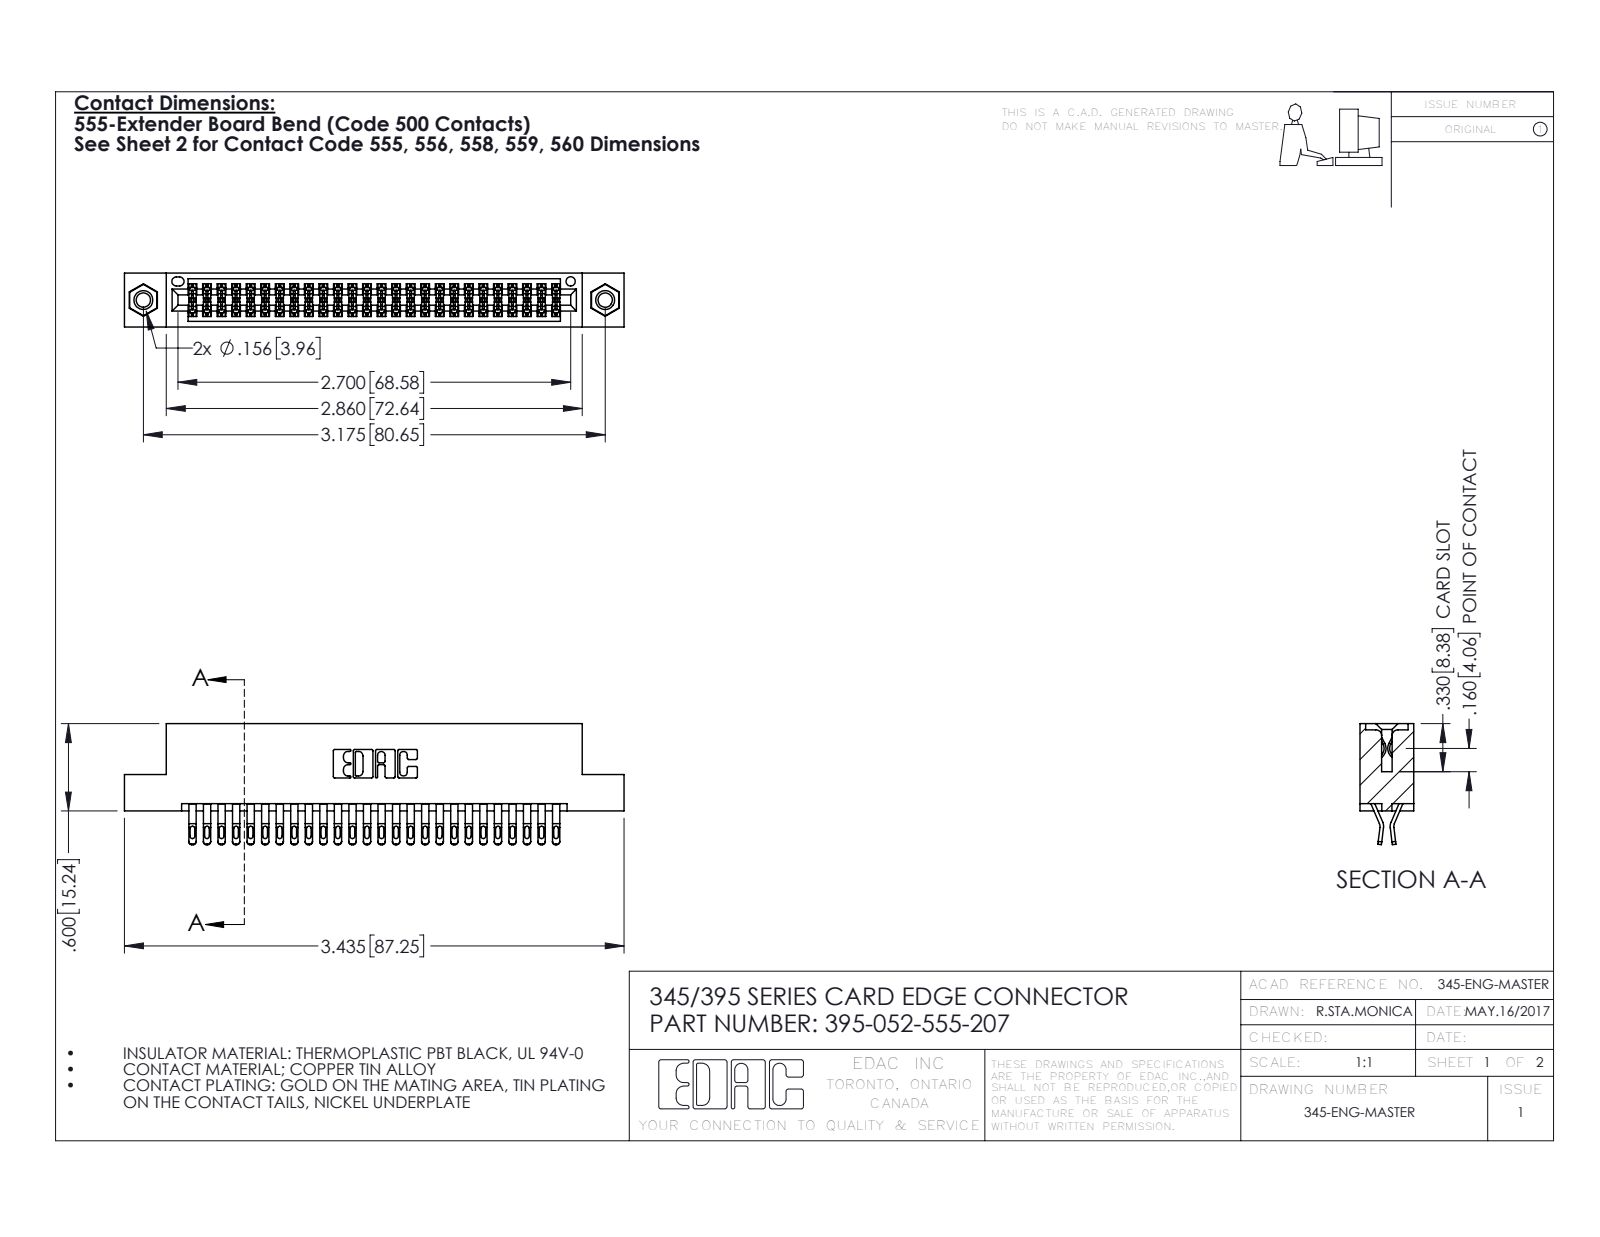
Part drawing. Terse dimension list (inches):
name: 395-052-555-207; 345 Part_Flush Mounting Lugs - 0.156 Dia-TI; 345-292-001_555 Tail; 345-250-001_345-250-005-103
written by: SolidWorks 2016 (CONFIG_CONTROL_DESIGN)
unit: in
bodies: 55 solids, 3098 faces (1724 planar, 1358 cylindrical, 16 other)
size: 3.435 × 0.832 × 0.37
volume: 0.517 in³; area: 19.77 in²
holes: 2× ⌀0.098, 2× ⌀0.125, 2× ⌀0.156, 1× ⌀0.064
bosses: 2× ⌀0.155
rounds: 130× R0.016, 104× R0.02, 78× R0.006, 22× R0.01, 6× R0.007, 6× R0.031, 3× R0.026, 2× R0.01
face distances: 0.072, 0.298, 0.2, 0.37, 0.025, 0.098, 0.272, 0.225, 0.175, 0.149
hole spacings: 0.27, 2.94, 3.175
